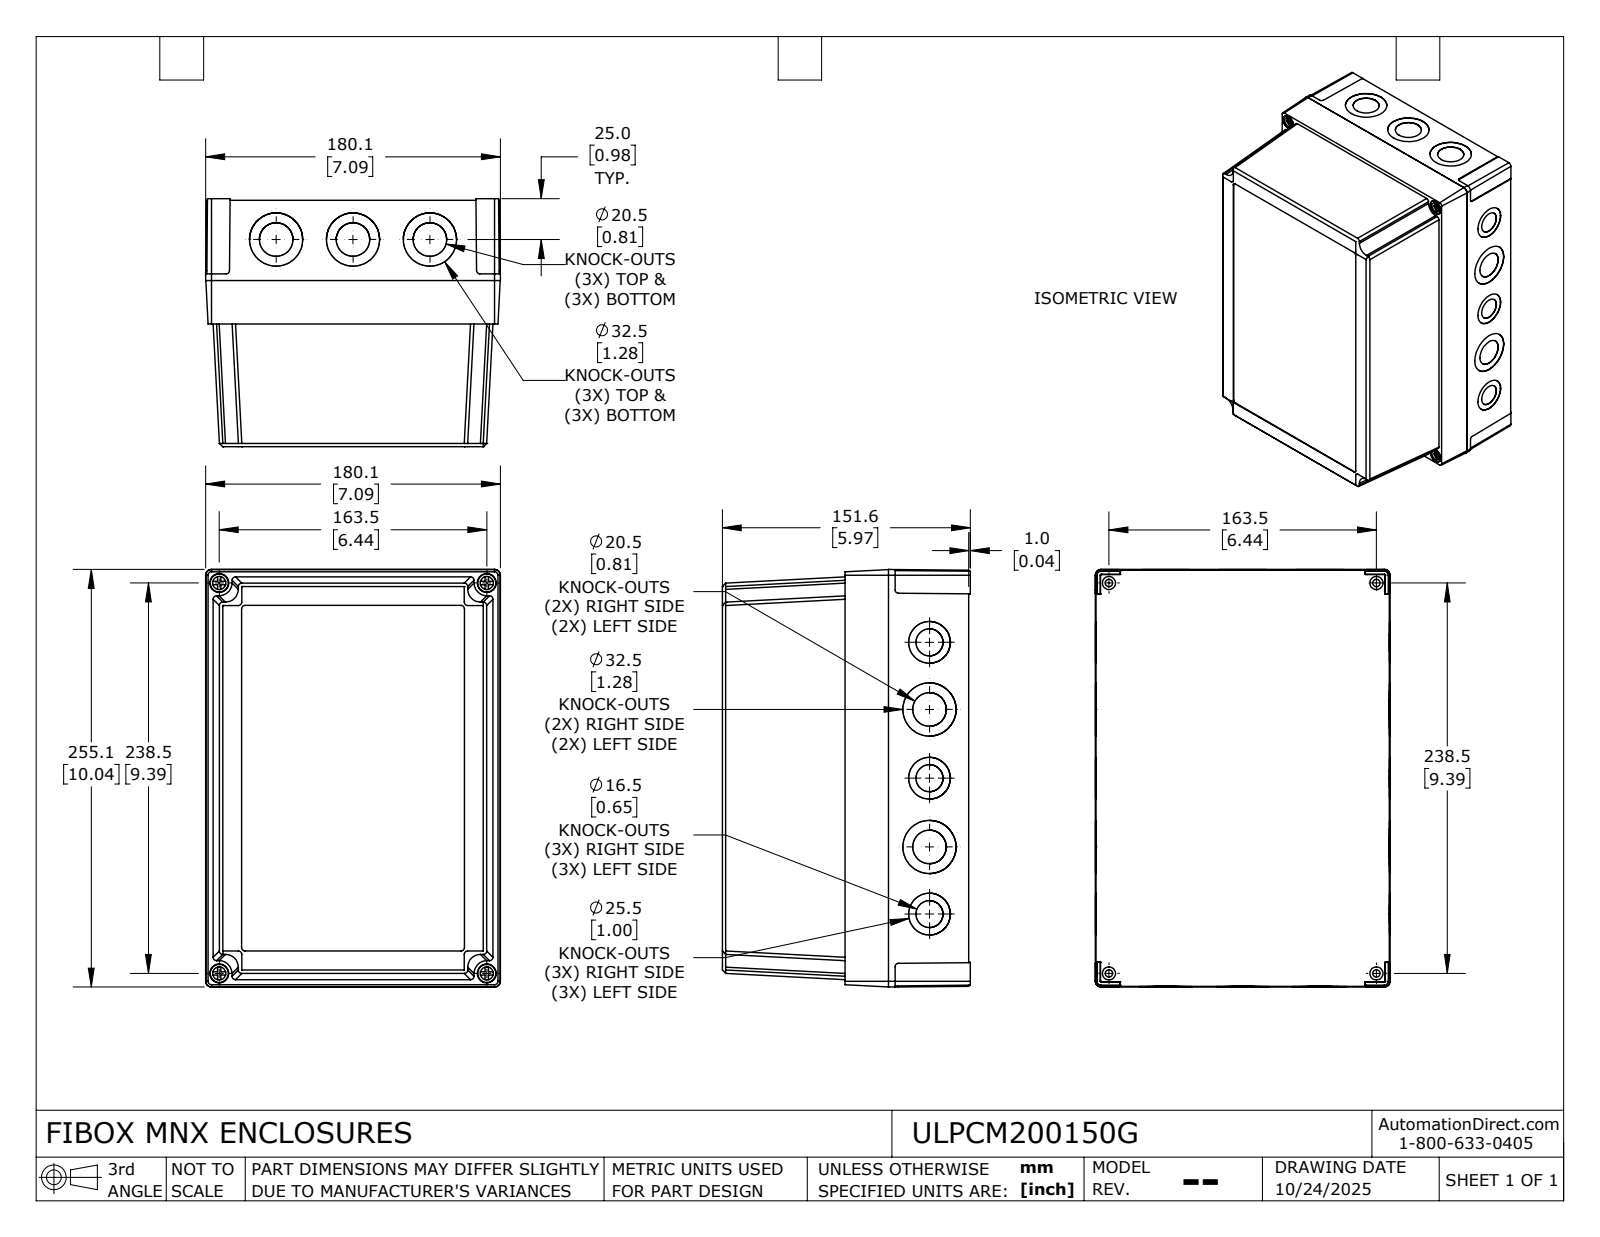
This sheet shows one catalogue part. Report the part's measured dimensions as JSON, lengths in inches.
{"part_name": "ULPCM200150G_Default", "step_written_by": "SolidWorks 2024 (CONFIG_CONTROL_DESIGN)", "units": "inches", "bodies": {"solids": 6, "faces": 749, "planar": 395, "cylindrical": 296, "other": 58}, "overall_size": [10.043, 7.091, 5.969], "volume_in3": 35.61, "surface_area_in2": 679.5, "round_holes": [[0.126, 20], [0.157, 20], [0.807, 10], [1.28, 10], [0.65, 6], [1.004, 6], [0.177, 4], [0.315, 4], [0.457, 4]], "round_bosses_or_shafts": [[0.315, 16], [0.433, 4], [0.283, 4], [0.276, 4]], "partial_cylinders_radius": [[0.079, 8], [0.083, 8], [0.112, 6], [0.042, 4], [0.197, 4], [0.307, 4], [0.046, 2]], "face_to_face_distances": [0.059, 0.118, 5.811, 5.693, 0.098, 5.909, 5.791, 0.165, 0.18, 0.12], "hole_center_spacings": [4.921, 1.939, 5.046, 0.812, 0.872, 1.046, 1.333, 1.508]}
